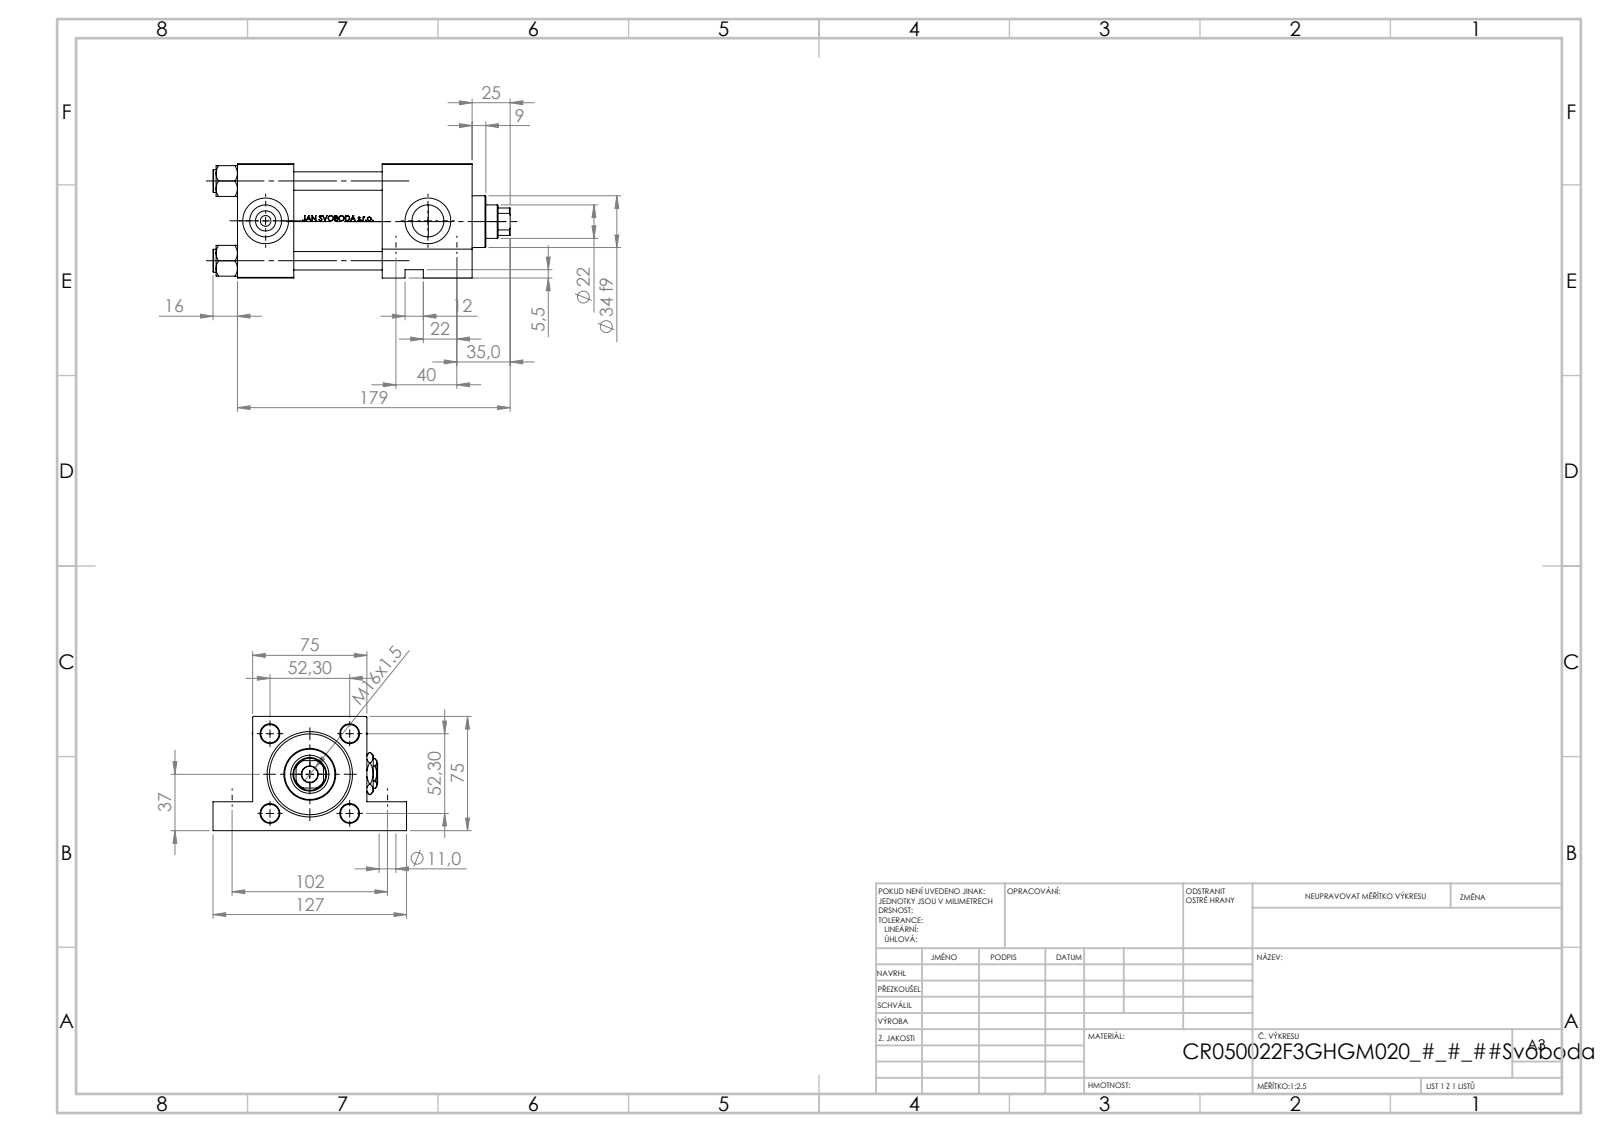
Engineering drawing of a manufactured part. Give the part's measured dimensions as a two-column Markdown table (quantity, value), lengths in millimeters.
| quantity | value |
| --- | --- |
| part name | V215CR_F_TYCINKA; V215CR_F_Body; NUT_M5_F; V215_VC_A (+2 more) |
| STEP written by | SolidWorks 2019 (CONFIG_CONTROL_DESIGN) |
| units | millimeters |
| bodies | 13 solids, 1199 faces (483 planar, 134 cylindrical, 582 other) |
| overall size | 195 × 127 × 75 |
| volume | 702 130 mm³ |
| surface area | 160 606 mm² |
| round holes (diameter × count) | 12 × 4, 20.96 × 3, 30 × 3, 7 × 2, 11 × 2, 11 × 2, 10.5 × 1, 17 × 1, 22 × 1, 25 × 1, 41 × 1, 50 × 1 |
| round bosses / shafts (diameter × count) | 15 × 4, 56 × 1, 34 × 1 |
| partial cylindrical surfaces (radius × count) | 10.5 × 1 |
| main face-to-face distances | 75, 37, 154, 117, 95, 58, 59, 19, 56, 125.3 |
| hole center spacings | 52.3, 36.63, 37.34, 40, 73.96, 102, 109.56, 13 |
